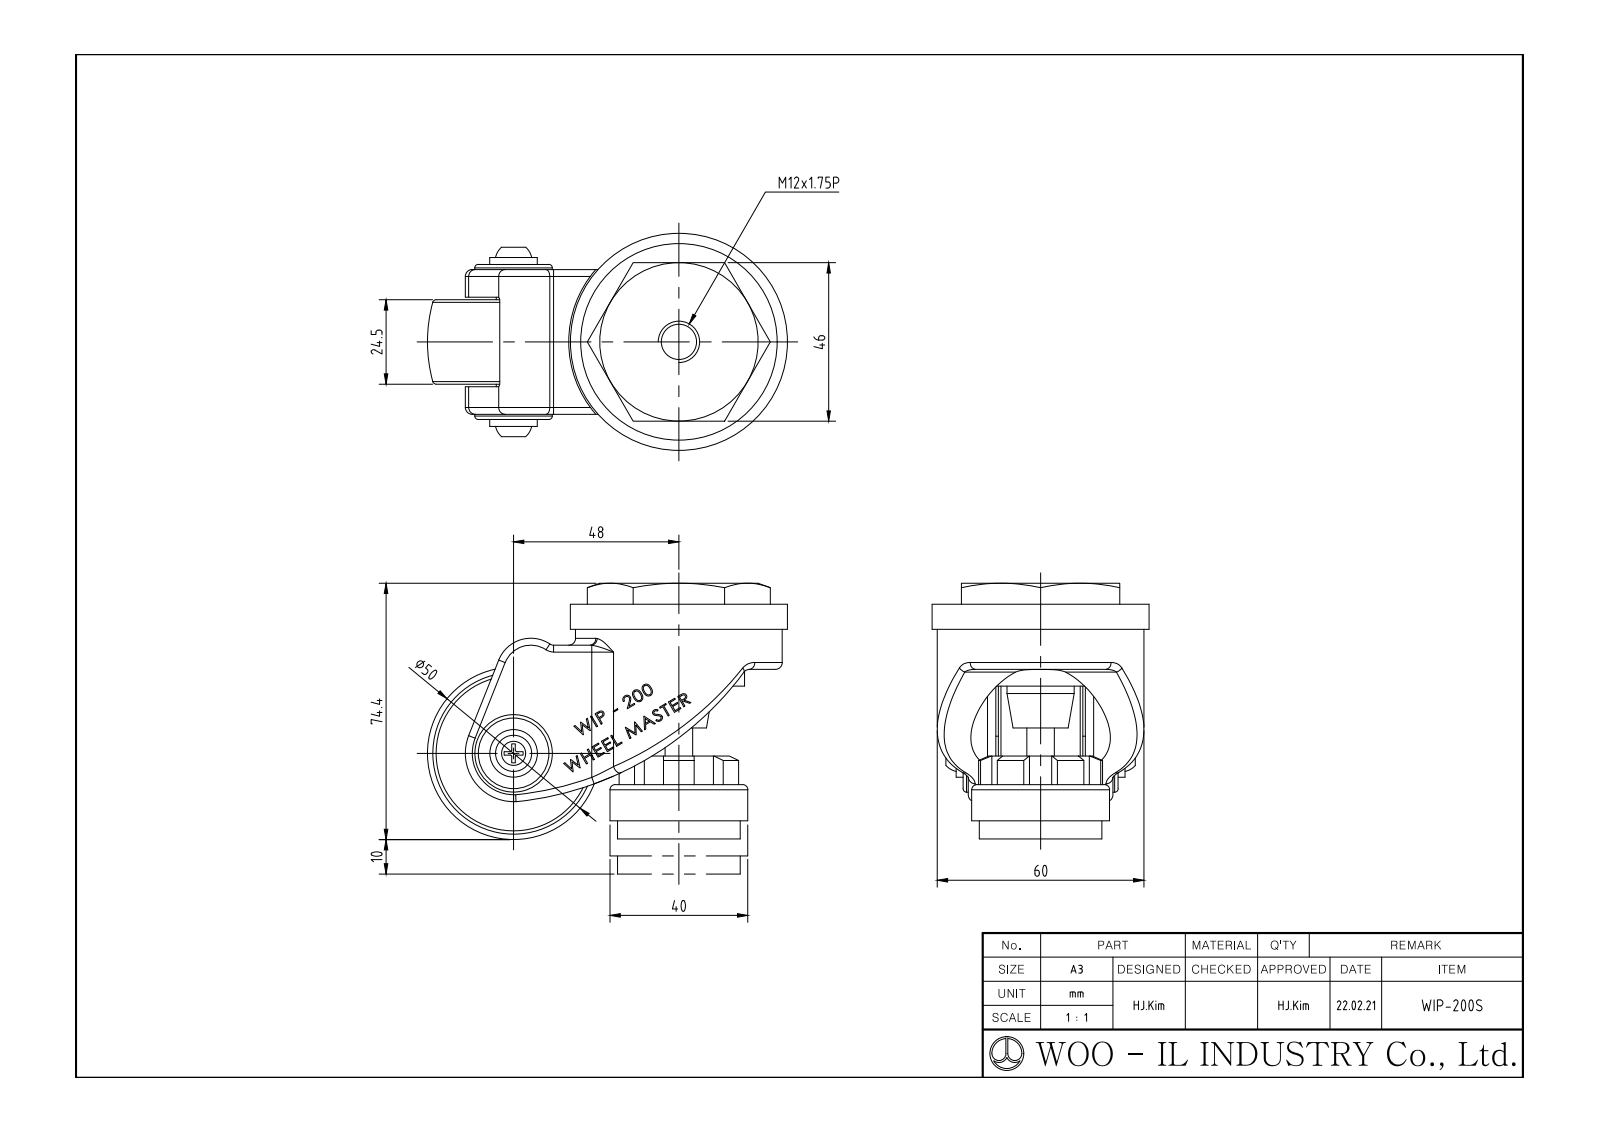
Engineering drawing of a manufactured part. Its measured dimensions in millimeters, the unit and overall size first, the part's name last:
Units: millimetres
Overall size (bounding box): 104.5 × 74.4 × 63
Round holes (diameter × count): ⌀10 ×1, ⌀10.4 ×1, ⌀22 ×1, ⌀27 ×1, ⌀31.64 ×1
Round bosses / shafts (diameter × count): ⌀63 ×1, ⌀60 ×1, ⌀40 ×1, ⌀38.1 ×1, ⌀35.6 ×1, ⌀29.64 ×1, ⌀25 ×1, ⌀22.5 ×1
Partial cylindrical surfaces — rounded edges, fillets, slot ends (radius × count): R0.3 ×9, R2 ×8, R7.53 ×6, R10 ×5, R0.5 ×4, R1 ×3, R9.5 ×2, R2.5 ×1
Main face-to-face distances: 0.75, 25.25, 8, 8.75, 33.25, 34, 24.5, 26, 6.1, 42
Volume: 192 007 mm³ · Surface area: 39 538 mm²
Bodies: 1 solid, 640 faces (306 planar, 165 cylindrical, 169 other)
Part name (STEP PRODUCT): WIP-200S
STEP written by: SolidWorks 2019 (AUTOMOTIVE_DESIGN)
